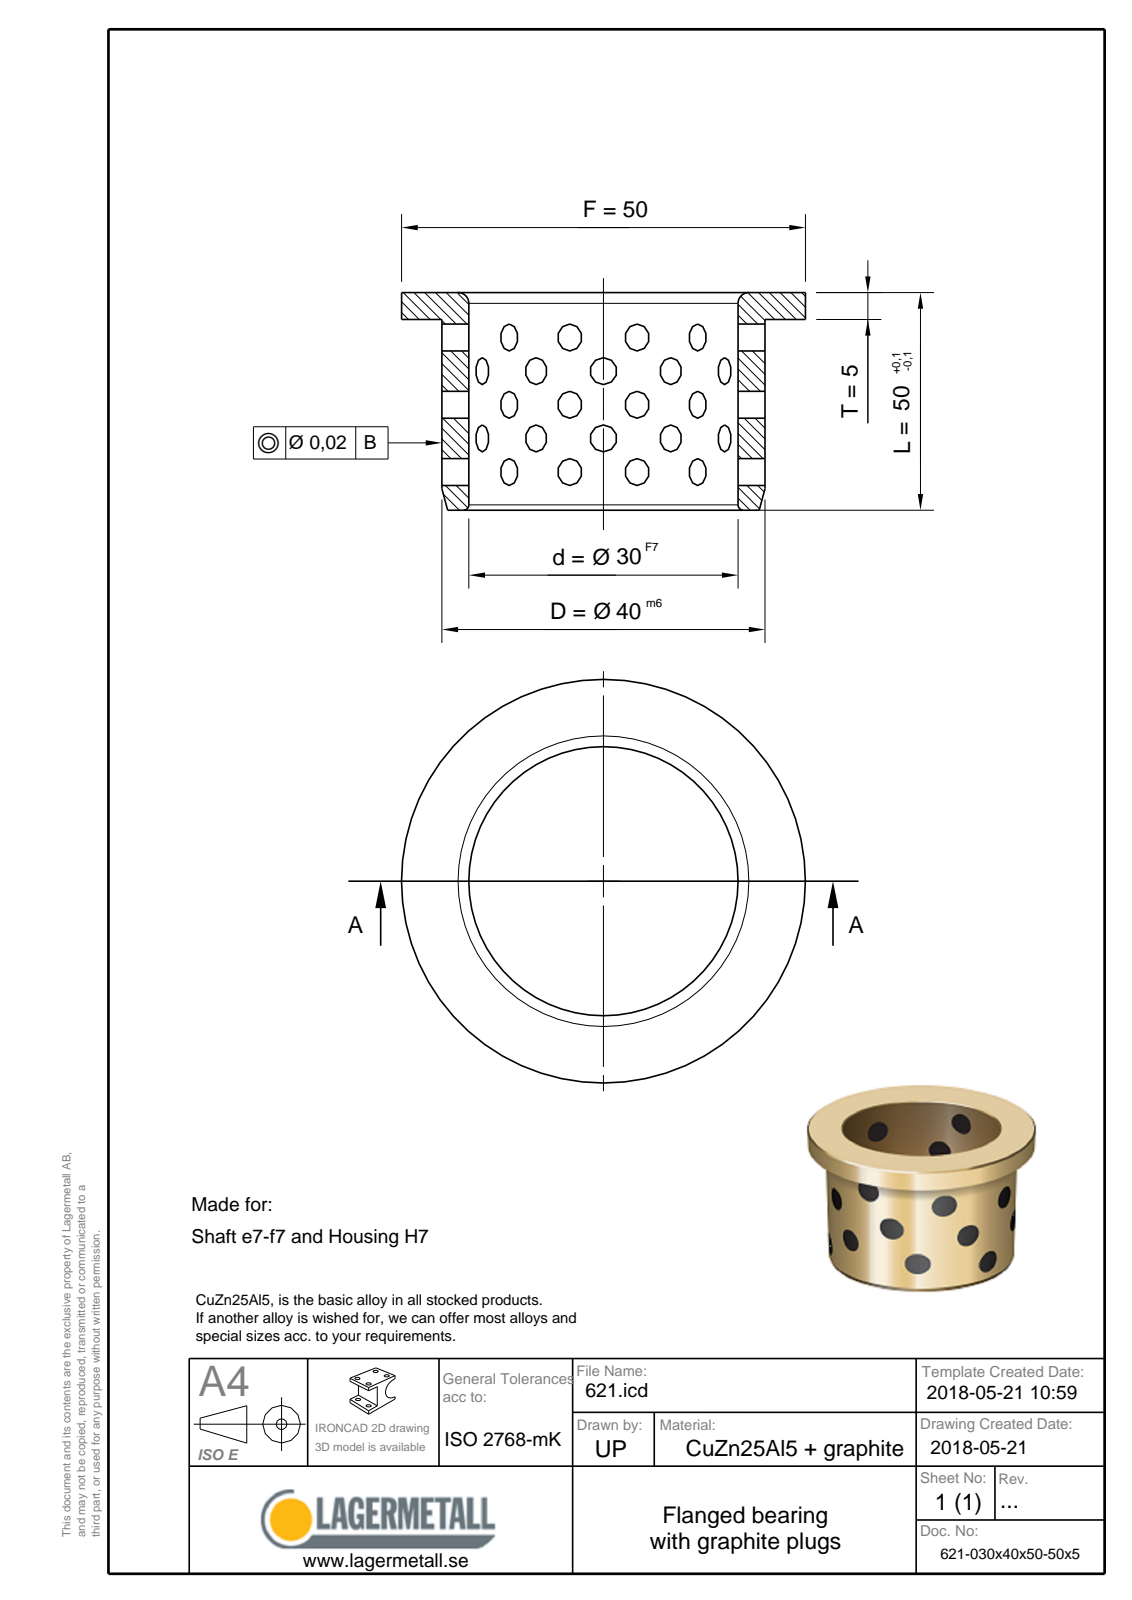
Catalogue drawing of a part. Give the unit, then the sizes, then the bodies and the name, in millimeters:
Units: millimetres
Overall size (bounding box): 50 × 50 × 50
Round holes (diameter × count): ⌀30 ×1
Round bosses / shafts (diameter × count): ⌀50 ×1, ⌀40 ×1
Main face-to-face distances: 5, 45, 50
Volume: 30 818 mm³ · Surface area: 13 440 mm²
Bodies: 1 solid, 9 faces (3 planar, 3 cylindrical, 3 other)
Part name (STEP PRODUCT): 621-030x40x50-50x5
STEP written by: Spatial InterOp 3D (CONFIG_CONTROL_DESIGN)
